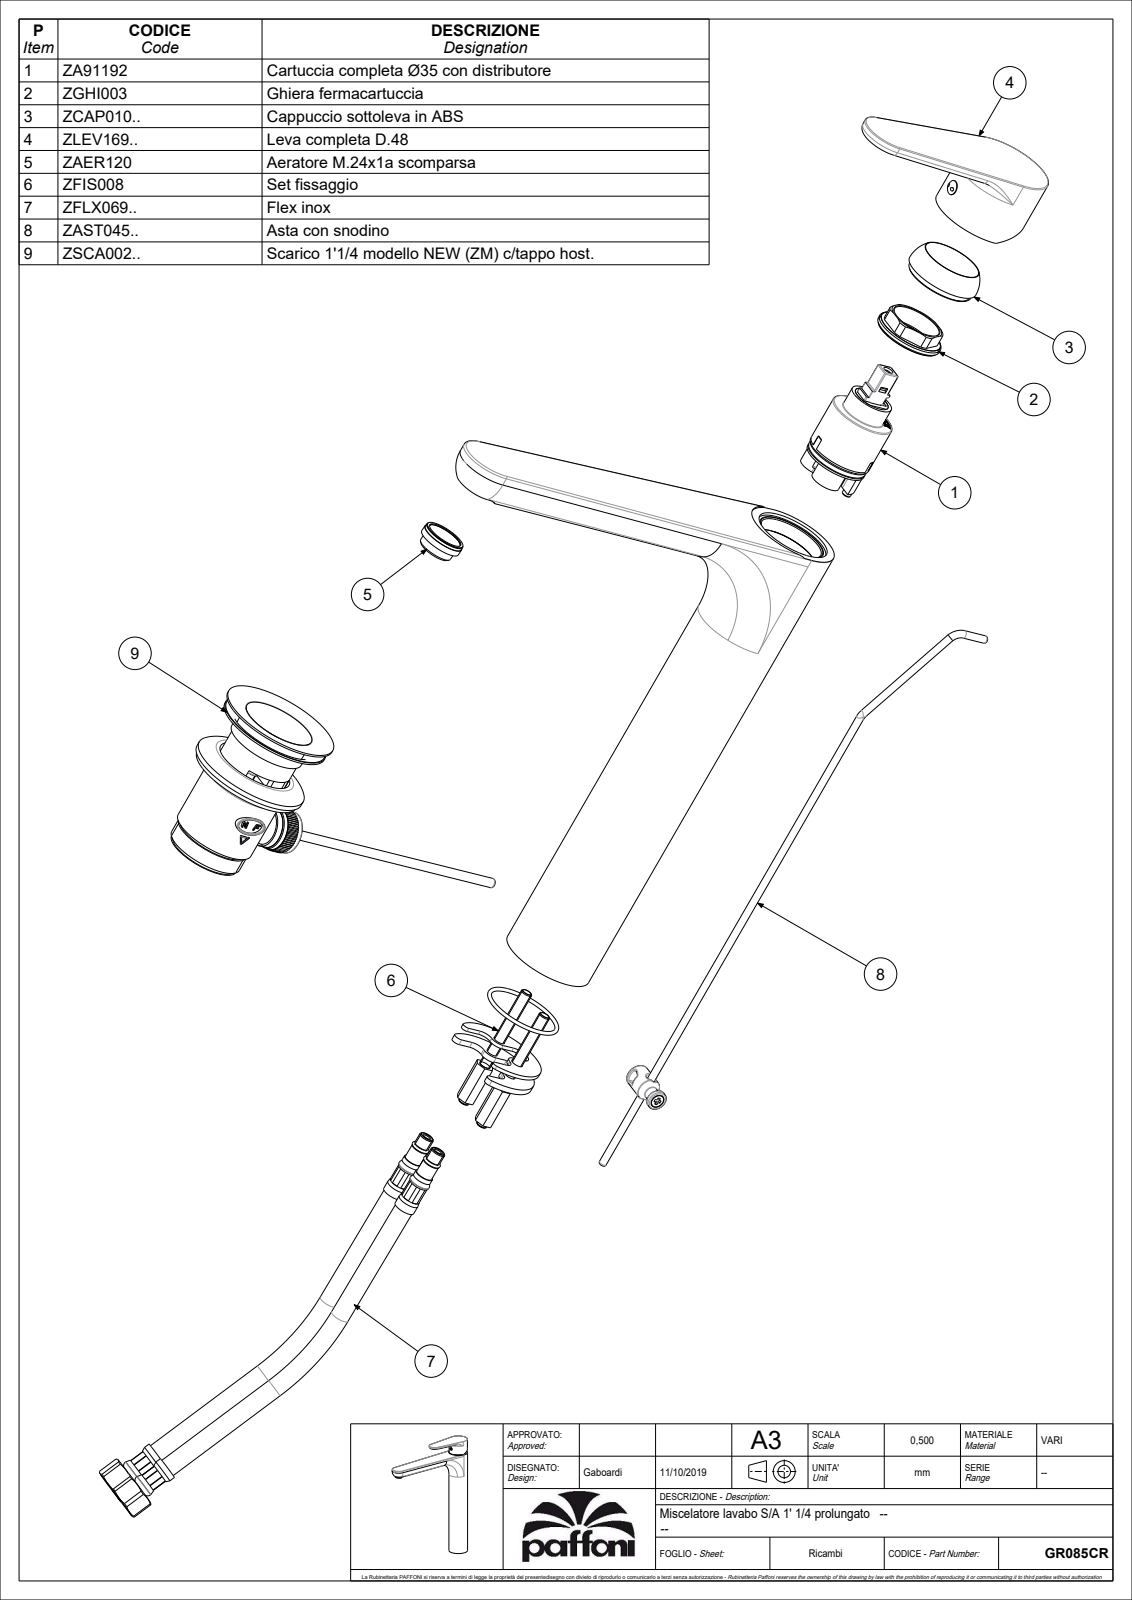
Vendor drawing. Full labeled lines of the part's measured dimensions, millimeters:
Part name (STEP PRODUCT): GR085CR
STEP written by: CREO PARAMETRIC BY PTC INC, 2020044 (CONFIG_CONTROL_DESIGN)
Units: millimetres
Bodies: 2 solids, 382 faces (109 planar, 123 cylindrical, 150 other)
Overall size (bounding box): 311.2 × 272.53 × 49
Volume: 238 410 mm³ · Surface area: 152 375 mm²
Round holes (diameter × count): ⌀5 ×4, ⌀3 ×1, ⌀4.2 ×1, ⌀16 ×1, ⌀19.5 ×1, ⌀25 ×1, ⌀31.5 ×1, ⌀33 ×1, ⌀34 ×1, ⌀35.7 ×1, ⌀43 ×1, ⌀43.5 ×1
Round bosses / shafts (diameter × count): ⌀4 ×2, ⌀49 ×1, ⌀48 ×1, ⌀38.5 ×1, ⌀23 ×1, ⌀18.8 ×1, ⌀7.6 ×1, ⌀5.5 ×1
Partial cylindrical surfaces — rounded edges, fillets, slot ends (radius × count): R1 ×32, R6 ×8, R0.5 ×2, R3 ×2, R5 ×2, R14.5 ×1, R15 ×1, R15.5 ×1
Main face-to-face distances: 3, 39.7, 36.7, 6, 2, 33.7, 30.7, 4, 2.2, 0.8
Hole centre spacings: 12.3, 13.57, 13.6, 13.45, 13.5, 22
